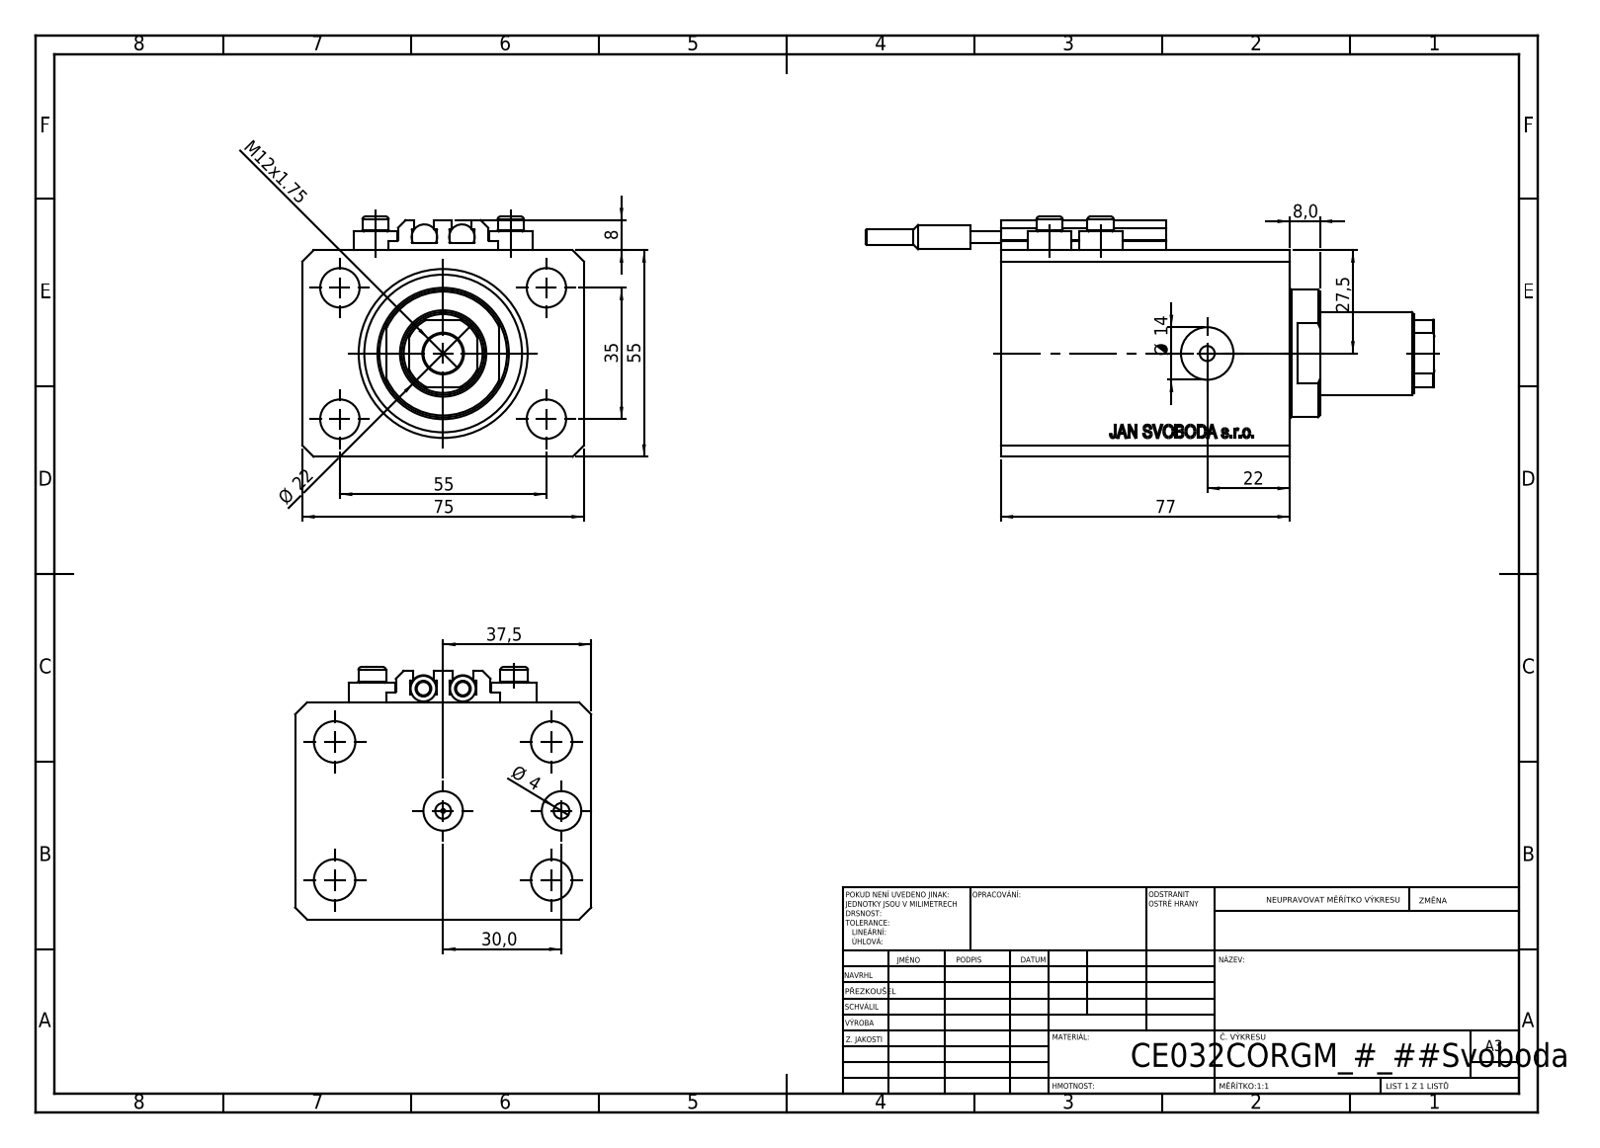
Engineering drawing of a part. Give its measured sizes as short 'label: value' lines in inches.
name: ALLEN BOLT V250CE; SWITCH_V250CE; V250CE_C_Body; V250CE_C_VCP (+1 more)
written by: SolidWorks 2019 (CONFIG_CONTROL_DESIGN)
unit: in
bodies: 10 solids, 1096 faces (538 planar, 104 cylindrical, 454 other)
size: 5.965 × 2.953 × 2.52
volume: 19.28 in³; area: 113.1 in²
holes: 8× ⌀0.157, 5× ⌀0.413, 2× ⌀0.394, 2× ⌀0.551, 1× ⌀0.049, 1× ⌀0.866, 1× ⌀1.26, 1× ⌀1.772
bosses: 4× ⌀0.457, 4× ⌀0.276, 2× ⌀0.268, 2× ⌀0.256, 2× ⌀0.157, 1× ⌀1.339
rounds: 10× R0.008, 1× R0.413
face distances: 2.165, 2.953, 3.031, 0.988, 2.043, 1.772, 1.26, 0.783, 0.118, 2.244
hole spacings: 1.283, 0.535, 0.696, 1.378, 1.417, 1.515, 2.165, 2.366
